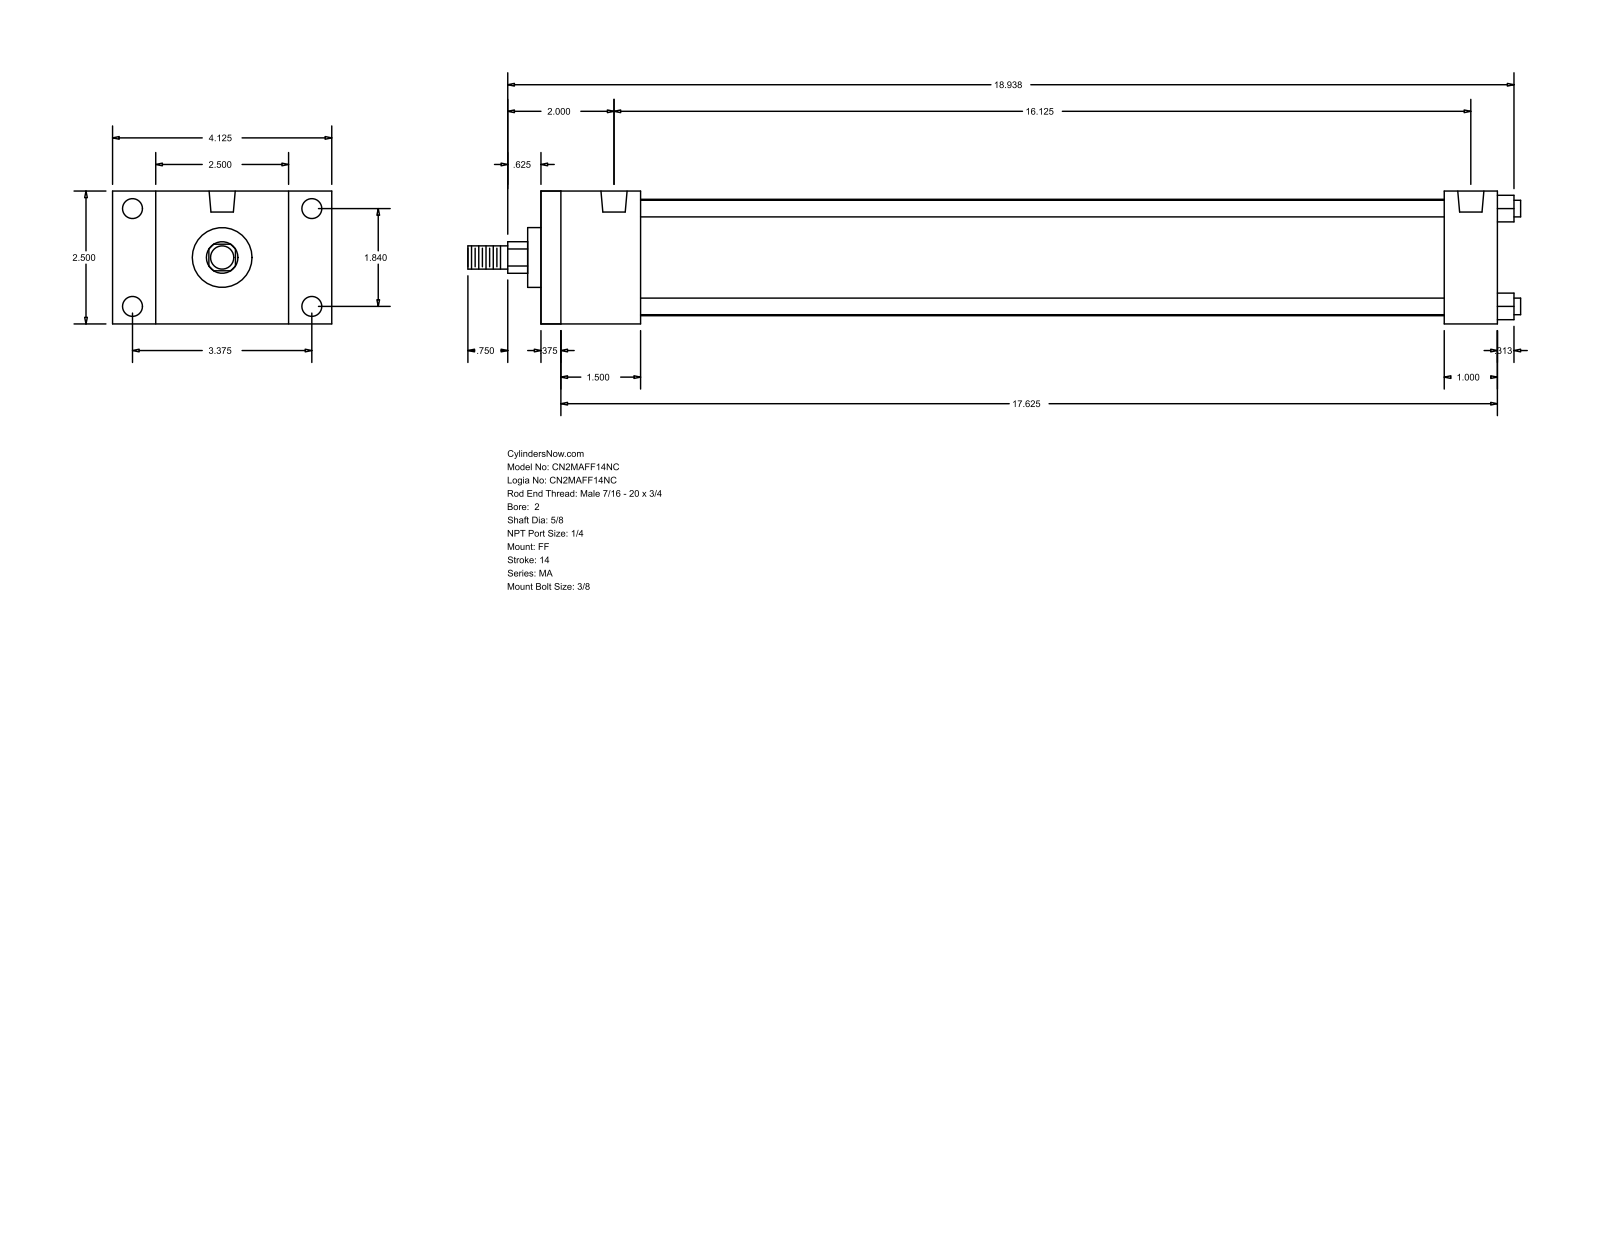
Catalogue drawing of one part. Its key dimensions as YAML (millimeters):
part_name: "MA_FF__0200_0.625"
step_written_by: "GSSL Pune (CONFIG_CONTROL_DESIGN)"
units: millimeters
bodies: {solids: 0, faces: 92, planar: 64, cylindrical: 28, other: 0}
overall_size: [503.24, 104.78, 63.5]
round_holes:
  - {diameter: 7.94, count: 4}
  - {diameter: 9.53, count: 4}
  - {diameter: 12.49, count: 2}
round_bosses_or_shafts:
  - {diameter: 7.94, count: 4}
  - {diameter: 55.63, count: 1}
  - {diameter: 28.57, count: 1}
  - {diameter: 15.88, count: 1}
  - {diameter: 11.11, count: 1}
partial_cylinders:
  - {radius: 7.54, count: 1}
face_to_face_distances: [63.5, 457.19, 9.52, 447.67, 38.1, 47.62, 431.8, 422.28, 384.18, 409.57]
hole_center_spacings: [46.74, 85.72, 97.63, 409.58]
